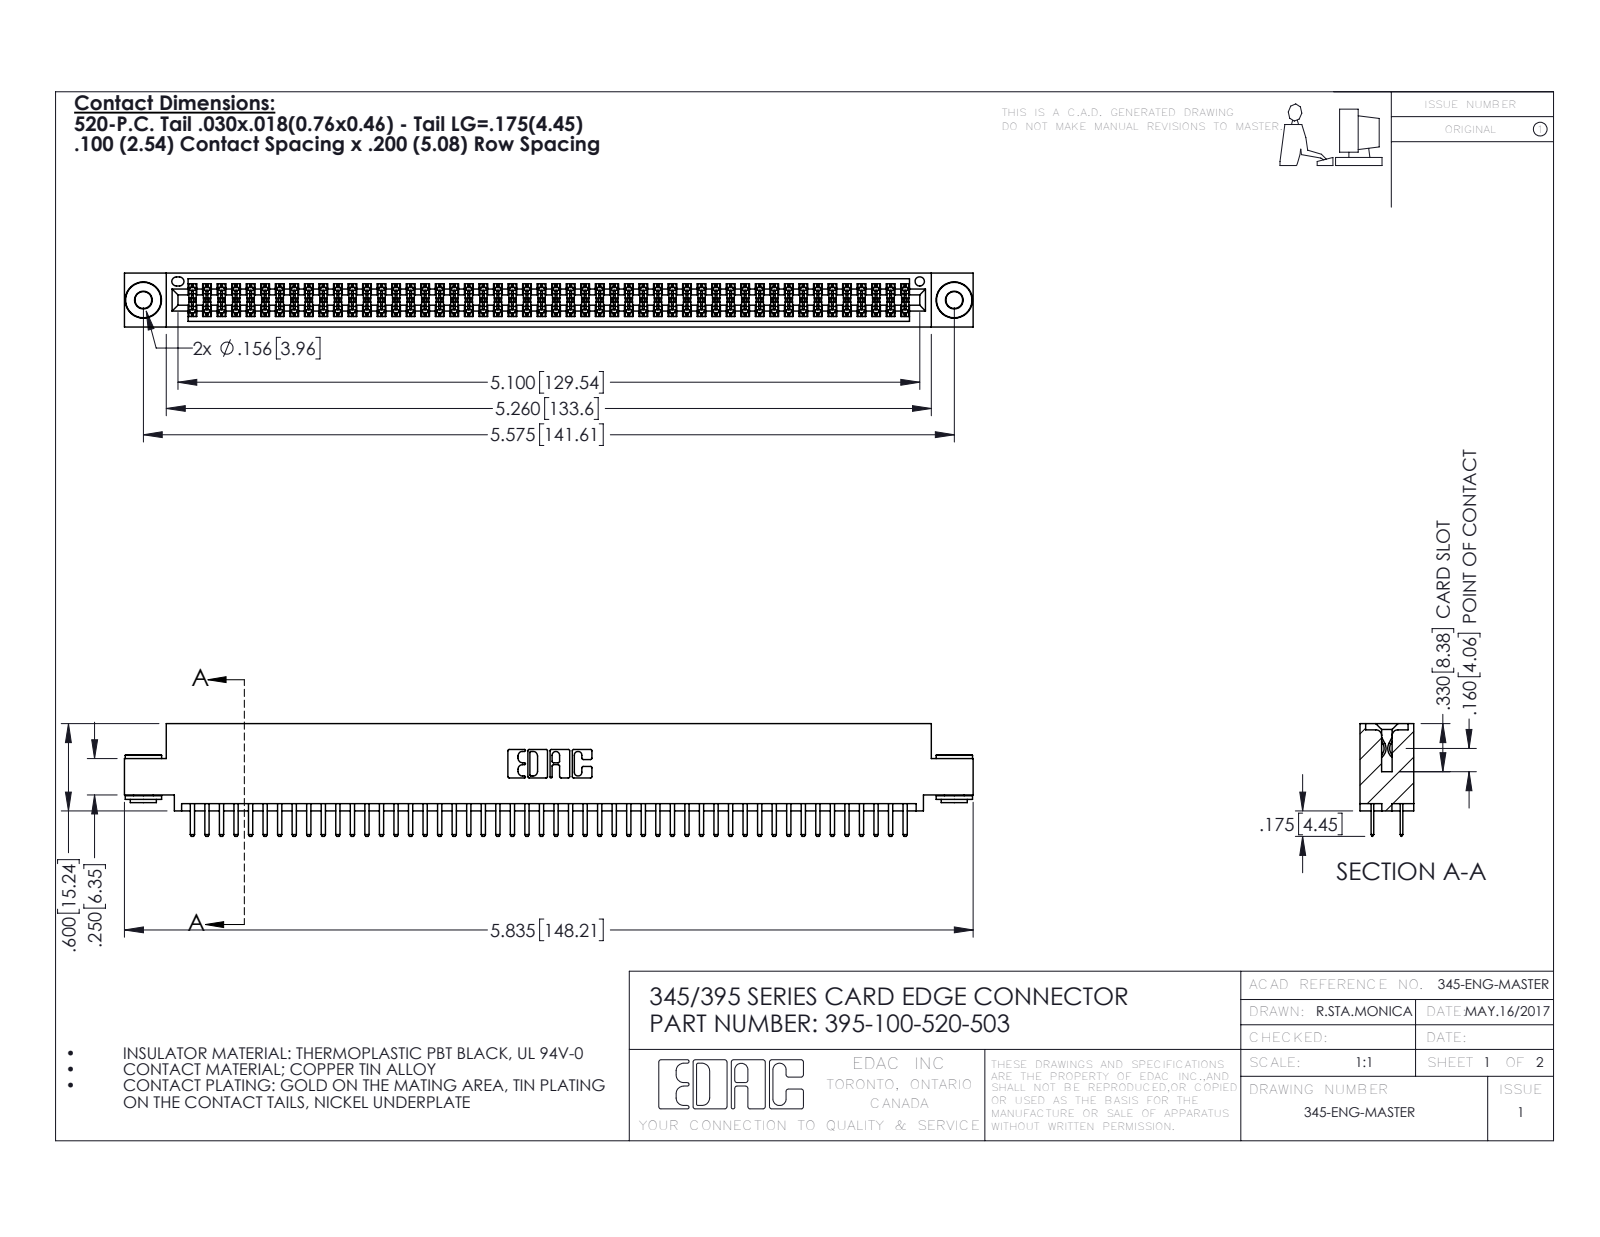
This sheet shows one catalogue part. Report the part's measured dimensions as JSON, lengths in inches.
{"part_name": "345-292-001_345-293-120; 345 Part_0.110 Offset - 0.156 Dia-TH; 395-100-520-503; 345-250-002_345-250-002-102", "step_written_by": "SolidWorks 2016 (CONFIG_CONTROL_DESIGN)", "units": "inches", "bodies": {"solids": 103, "faces": 5568, "planar": 3594, "cylindrical": 1966, "other": 8}, "overall_size": [5.835, 0.775, 0.37], "volume_in3": 0.877, "surface_area_in2": 33.49, "round_holes": [[0.116, 2], [0.156, 2], [0.064, 1]], "round_bosses_or_shafts": [[0.25, 2], [0.18, 2], [0.136, 2]], "partial_cylinders_radius": [[0.006, 150], [0.01, 104], [0.01, 22], [0.007, 6], [0.031, 6], [0.026, 3], [0.014, 2], [0.019, 2]], "face_to_face_distances": [0.072, 0.298, 0.2, 0.37, 0.025, 0.098, 0.272, 0.225, 0.022, 0.072], "hole_center_spacings": [0.27, 5.339, 5.575]}
